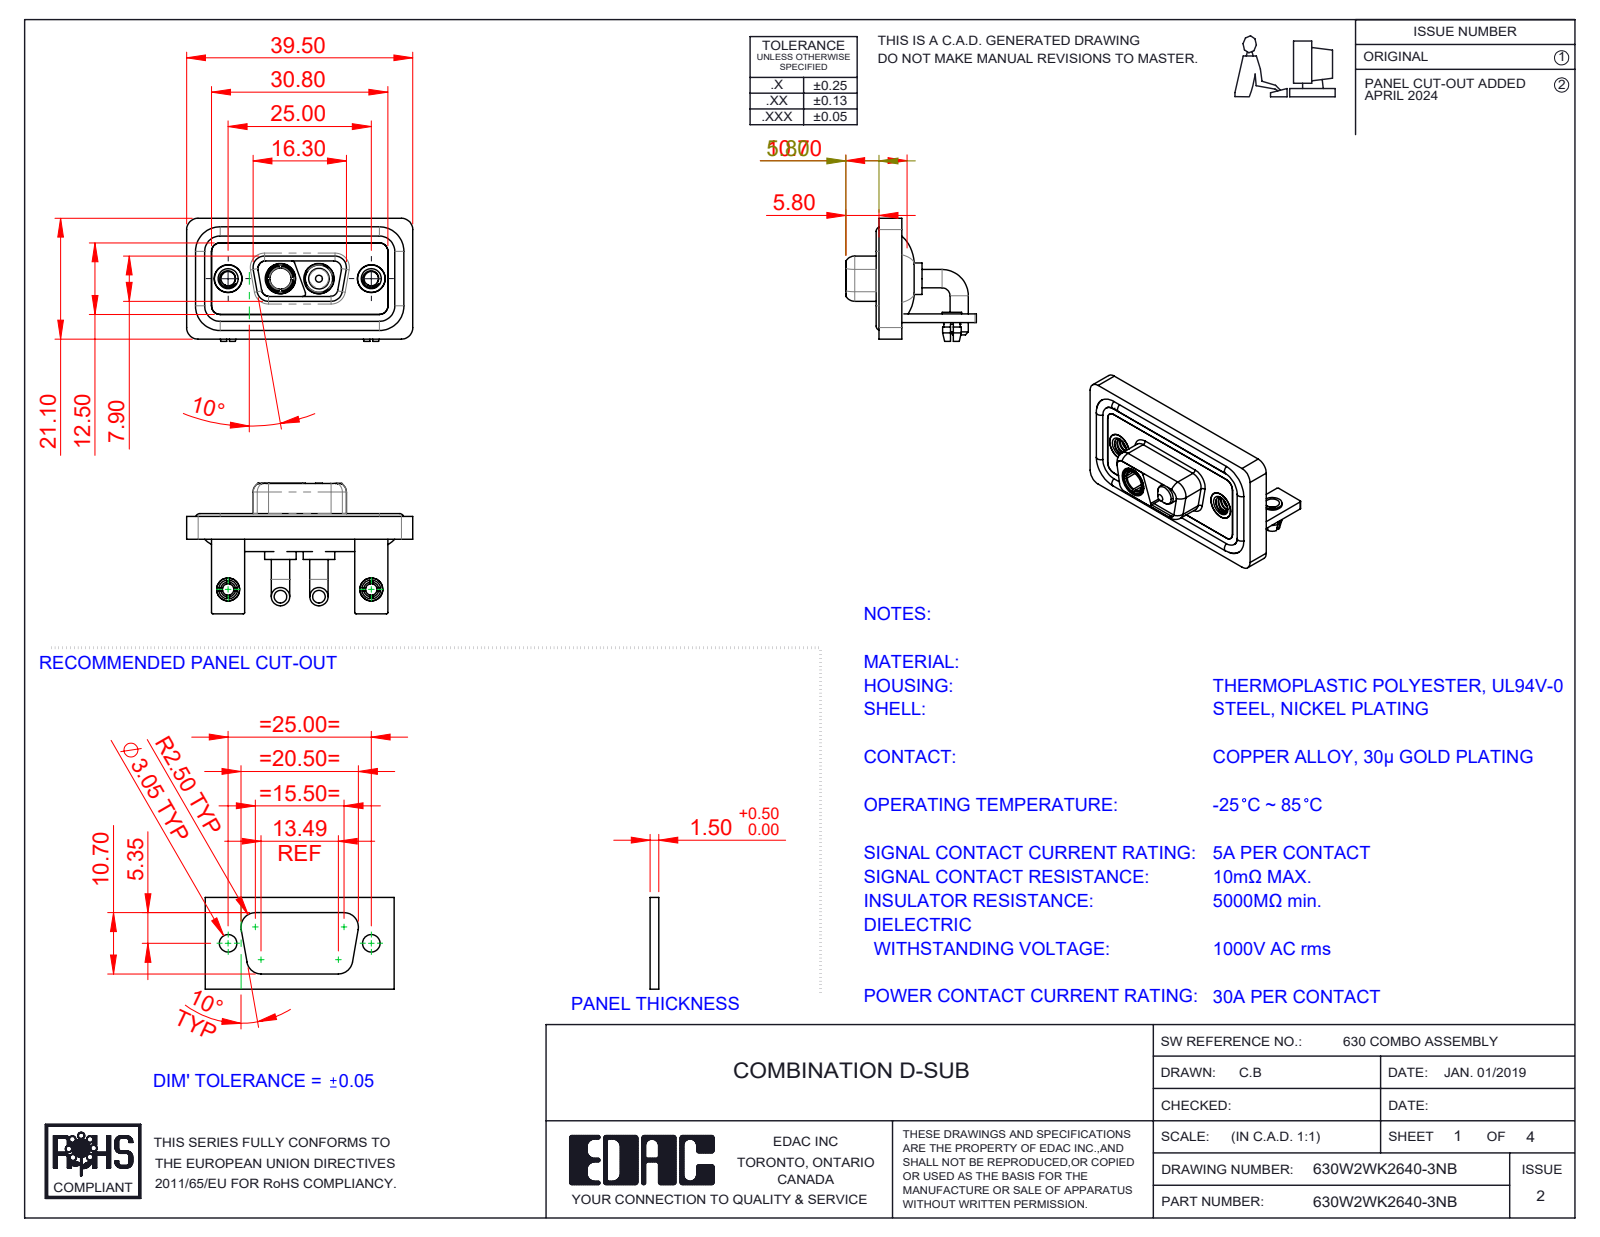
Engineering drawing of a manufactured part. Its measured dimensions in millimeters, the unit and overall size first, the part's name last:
Units: millimetres
Overall size (bounding box): 39.5 × 22.8 × 21.5
Round holes (diameter × count): ⌀2.5 ×4, ⌀4.85 ×4, ⌀2 ×2, ⌀3.2 ×2, ⌀4 ×2, ⌀4.05 ×2, ⌀5 ×2, ⌀5.3 ×2, ⌀3.7 ×1
Round bosses / shafts (diameter × count): ⌀3.2 ×4, ⌀1.6 ×4, ⌀5.5 ×2, ⌀5.2 ×2, ⌀4.95 ×2, ⌀4.8 ×2, ⌀4.75 ×2, ⌀4 ×2
Partial cylindrical surfaces — rounded edges, fillets, slot ends (radius × count): R2 ×19, R1.5 ×18, R0.25 ×16, R1.35 ×8, R1.6 ×8, R0.5 ×7, R0.6 ×4, R0.65 ×4
Main face-to-face distances: 0.4, 2.9, 1.5, 1.1, 3.7, 1.8, 0.8, 2.5, 1.6, 3.1
Hole centre spacings: 9.14, 15.86, 25, 6.72
Volume: 5 158 mm³ · Surface area: 8 480 mm²
Bodies: 15 solids, 642 faces (212 planar, 289 cylindrical, 141 other)
Part name (STEP PRODUCT): 630Combo Waterproof Housing_09 Contacts; 630Combo Housing_2WK2; 630Combo Board Lock_50 Contacts; 630Combo Shell Front_09 Contacts (+6 more)
STEP written by: SolidWorks 2023 (CONFIG_CONTROL_DESIGN)
